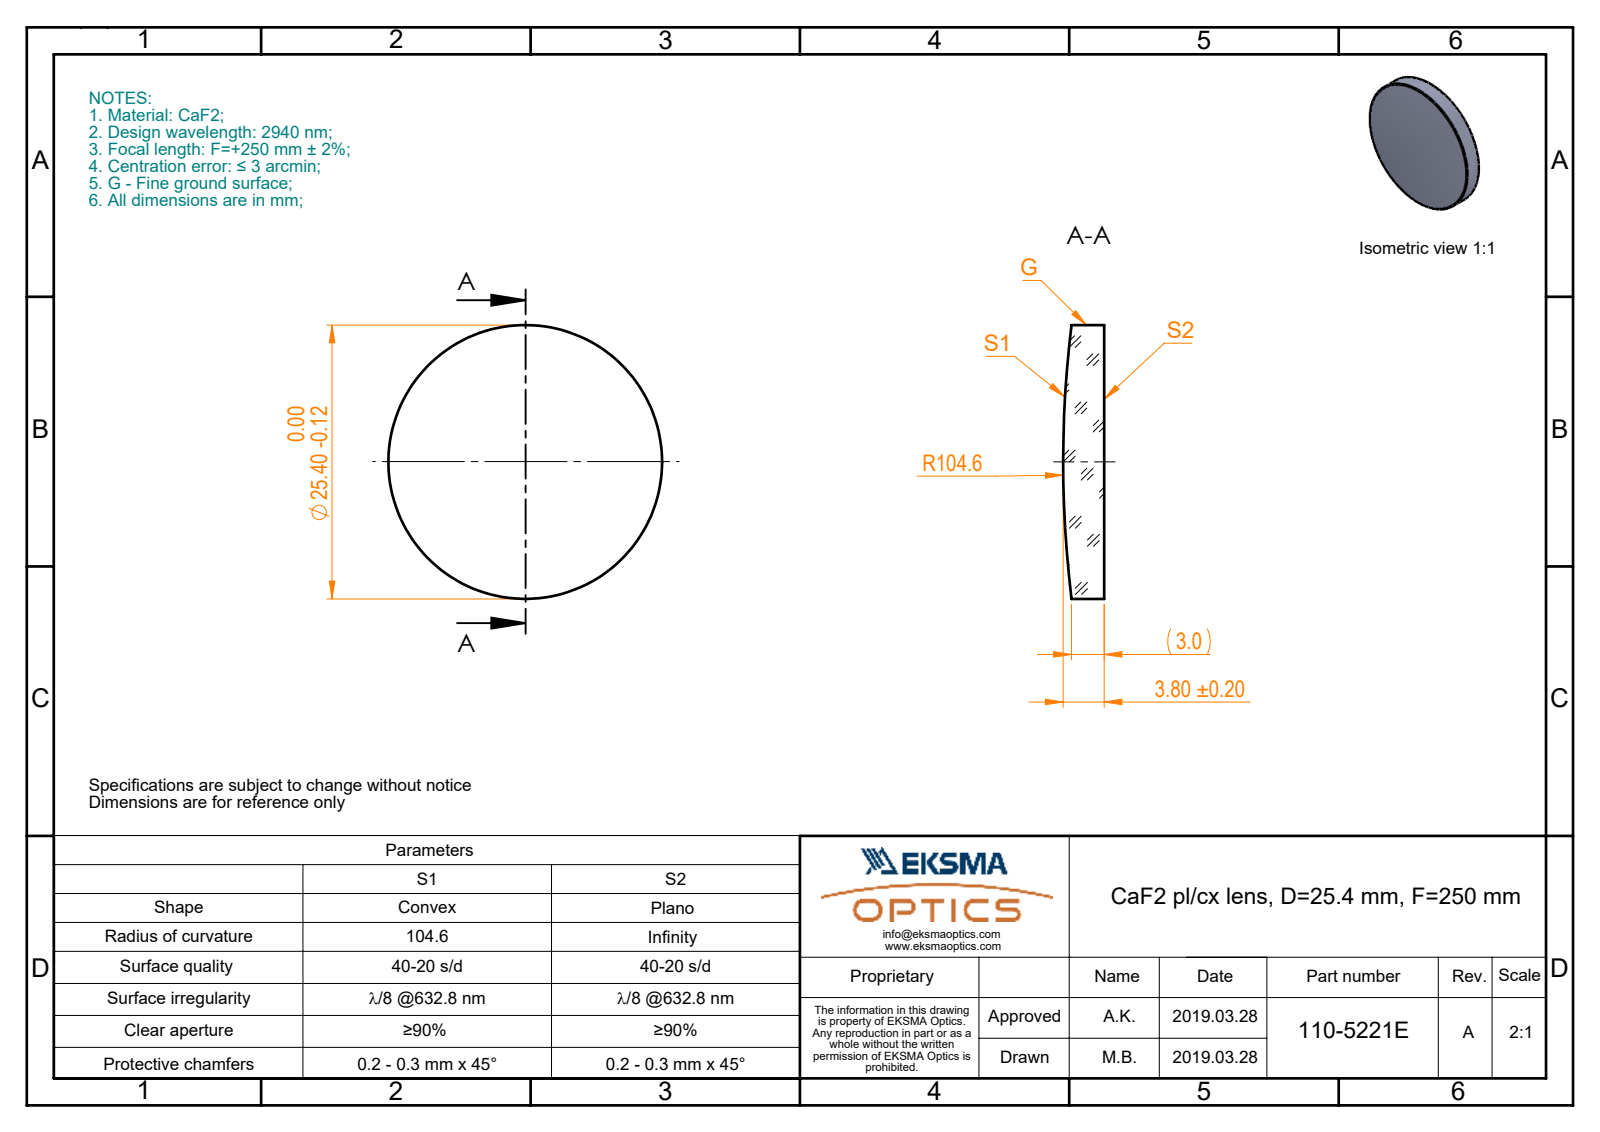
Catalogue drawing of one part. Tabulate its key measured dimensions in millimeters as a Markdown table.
| quantity | value |
| --- | --- |
| part name | 110-5221E CaF2 pl-cx 25.4 F250 |
| STEP written by | SolidWorks 2017 (CONFIG_CONTROL_DESIGN) |
| units | millimeters |
| bodies | 1 solid, 5 faces (1 planar, 2 cylindrical, 2 other) |
| overall size | 25.4 × 25.4 × 3.8 |
| volume | 1 730 mm³ |
| surface area | 1 257 mm² |
| round bosses / shafts (diameter × count) | 25.4 × 1 |
